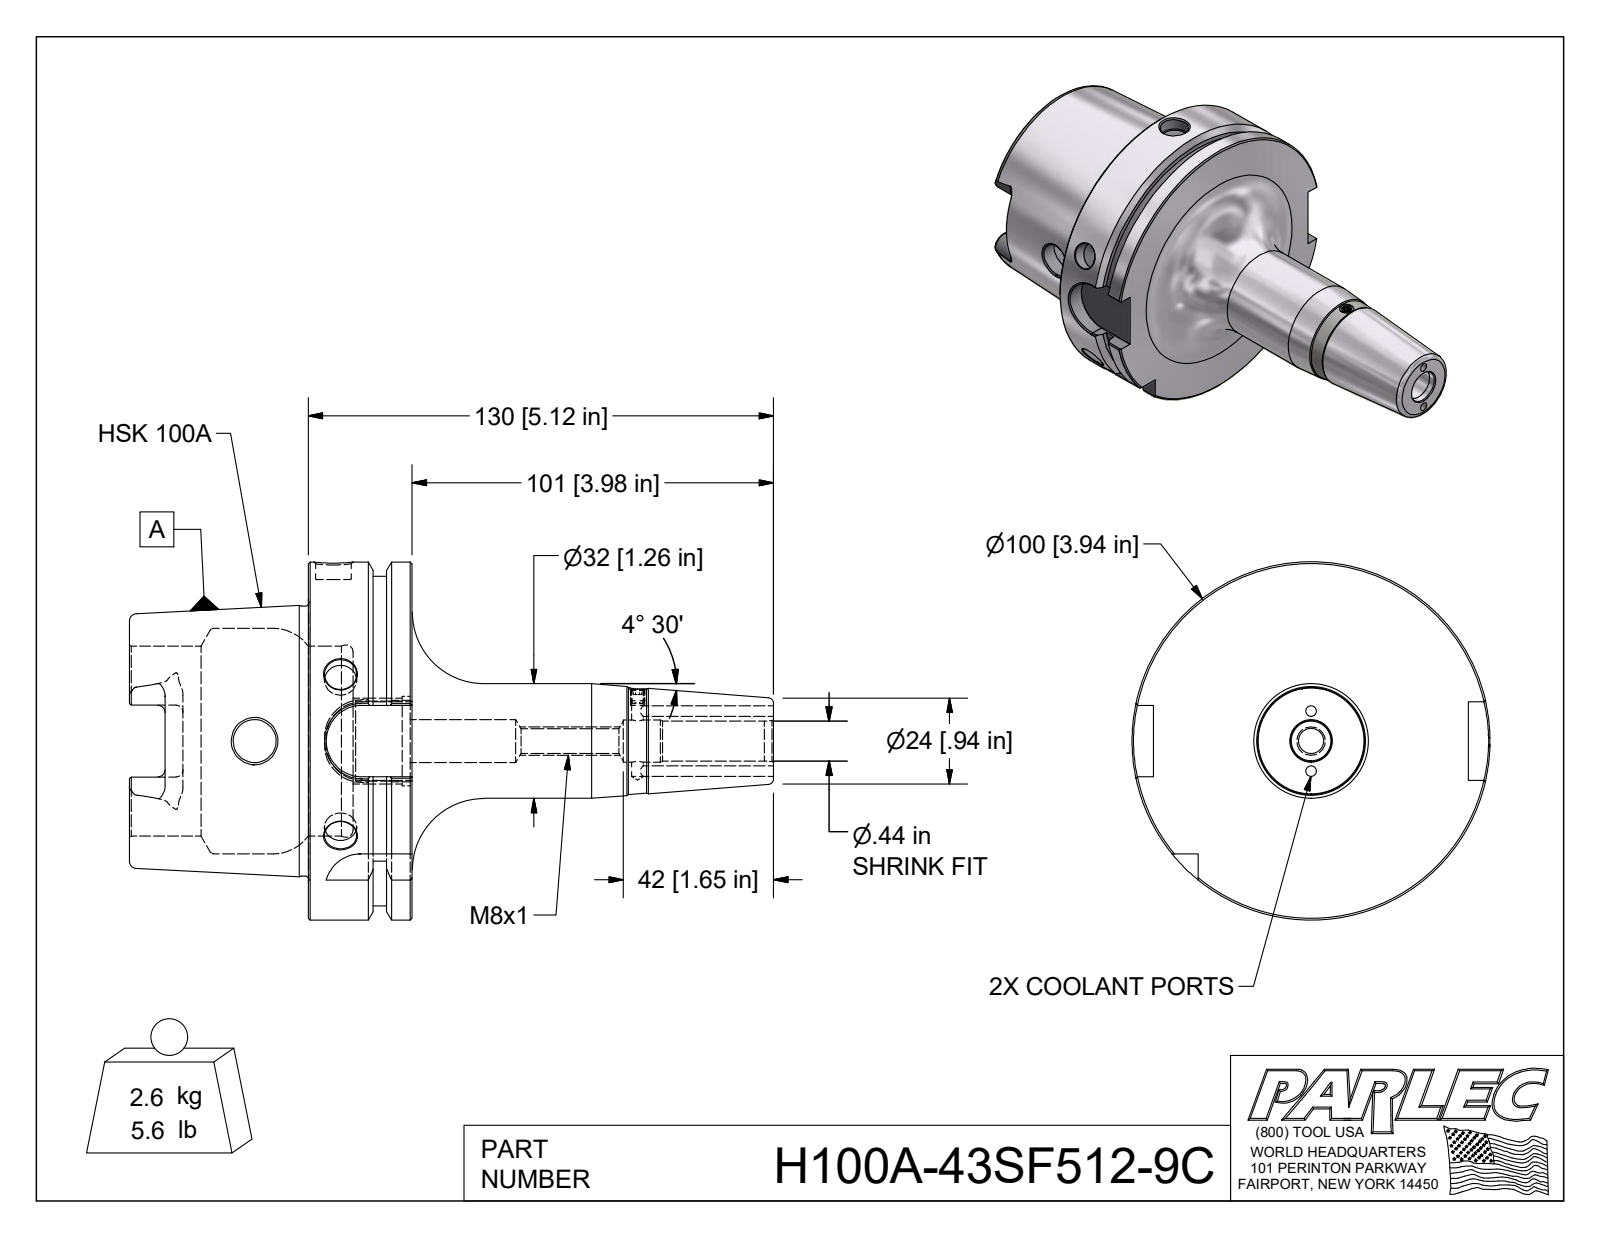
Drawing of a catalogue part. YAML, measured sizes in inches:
step_written_by: "Autodesk Inventor 2018 (AUTOMOTIVE_DESIGN)"
units: inches
bodies: {solids: 1, faces: 154, planar: 49, cylindrical: 42, other: 63}
overall_size: [7.087, 3.937, 3.937]
volume: 19.97
surface_area: 96.78
round_holes:
  - {diameter: 0.118, count: 2}
  - {diameter: 0.354, count: 2}
  - {diameter: 0.128, count: 1}
  - {diameter: 0.197, count: 1}
  - {diameter: 0.272, count: 1}
  - {diameter: 0.394, count: 1}
  - {diameter: 0.437, count: 1}
  - {diameter: 0.467, count: 1}
  - {diameter: 0.472, count: 1}
  - {diameter: 0.472, count: 1}
  - {diameter: 0.881, count: 1}
  - {diameter: 0.985, count: 1}
round_bosses_or_shafts:
  - {diameter: 3.937, count: 1}
  - {diameter: 3.622, count: 1}
  - {diameter: 2.967, count: 1}
  - {diameter: 1.26, count: 1}
partial_cylinders:
  - {radius: 0.079, count: 6}
  - {radius: 0.192, count: 4}
  - {radius: 0.394, count: 4}
face_to_face_distances: [1.142, 0.492, 0.65, 1.969, 2.461, 3.11, 3.465, 2.83, 0.861, 0.369]
hole_center_spacings: [0.33, 0.66, 3.346]
